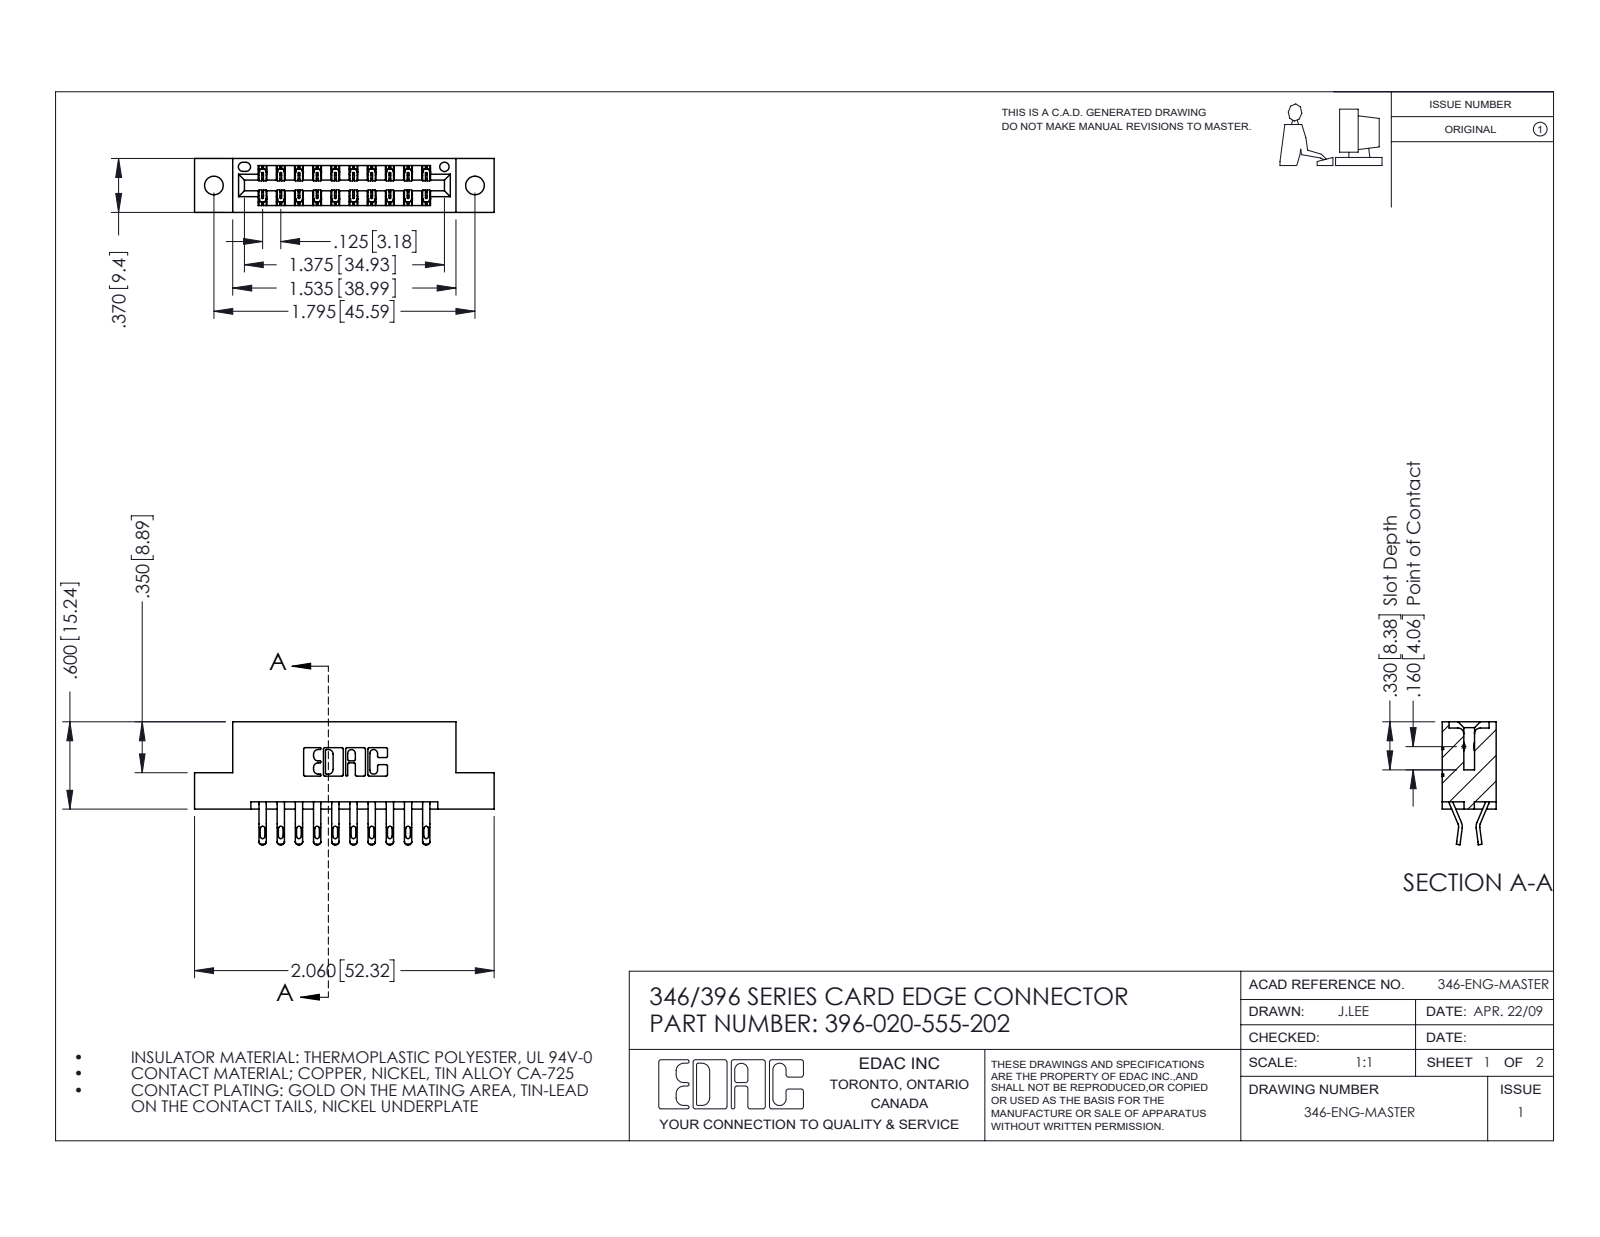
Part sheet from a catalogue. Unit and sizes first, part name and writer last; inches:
Units: inches
Overall size (bounding box): 2.06 × 0.845 × 0.37
Round holes (diameter × count): ⌀0.128 ×2, ⌀0.064 ×1
Partial cylindrical surfaces — rounded edges, fillets, slot ends (radius × count): R0.016 ×40, R0.02 ×40, R0.006 ×30, R0.01 ×22, R0.007 ×6, R0.031 ×6, R0.026 ×3, R0.01 ×2
Main face-to-face distances: 0.25, 0.048, 0.322, 0.37, 0.025, 0.072, 0.298, 0.275, 0.148, 0.222
Hole centre spacings: 0.246, 1.59, 1.795
Volume: 0.297 in³ · Surface area: 9.51 in²
Bodies: 21 solids, 1282 faces (736 planar, 546 cylindrical, 0 other)
Part name (STEP PRODUCT): 396-020-555-202; 346 Part_Flush Mounting Lugs - 0.128 Dia; 345-292-001_555 Tail
STEP written by: SolidWorks 2016 (CONFIG_CONTROL_DESIGN)
